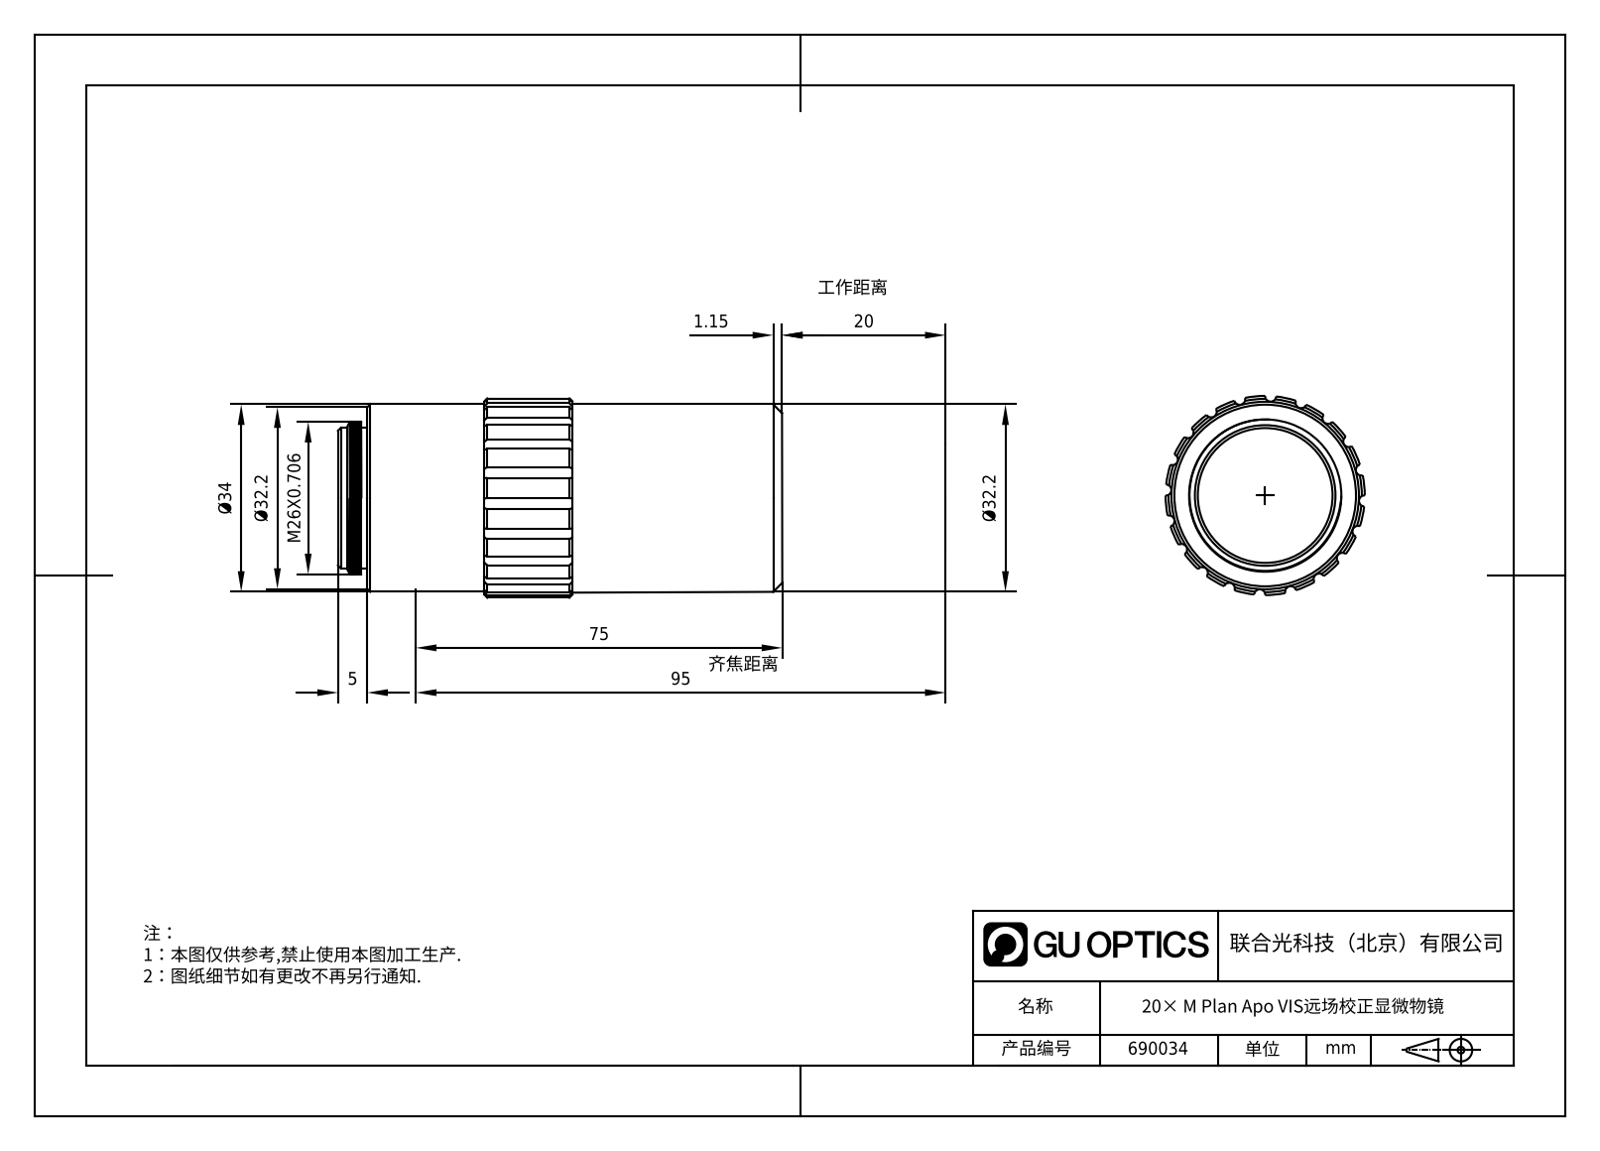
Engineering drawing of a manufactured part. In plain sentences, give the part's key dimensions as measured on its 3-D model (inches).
The part is named "690034". Its 3-D file was written by "SolidWorks 2020 (CONFIG_CONTROL_DESIGN)". It is 4 solids with 316 faces: 146 planar, 78 cylindrical and 92 other. Overall it measures 3.126 by 1.337 by 1.337 inches. Its volume is 3.784 cubic inches and its surface area 23.2 square inches. Round holes: 1 of diameter 0.844. Round bosses or shafts: 1 of diameter 1.268, 1 of diameter 1.26, 1 of diameter 1.024, 1 of diameter 0.945. Partial cylindrical surfaces (rounded edges, fillets, slot ends): 16 of radius 0.028, 1 of radius 0.63, 1 of radius 0.669. The main face-to-face distances are 2.902, 0.197, 3.014, 0.113, 0.084, 3.098, 2.817, 2.705, 0.039, 0.157.
